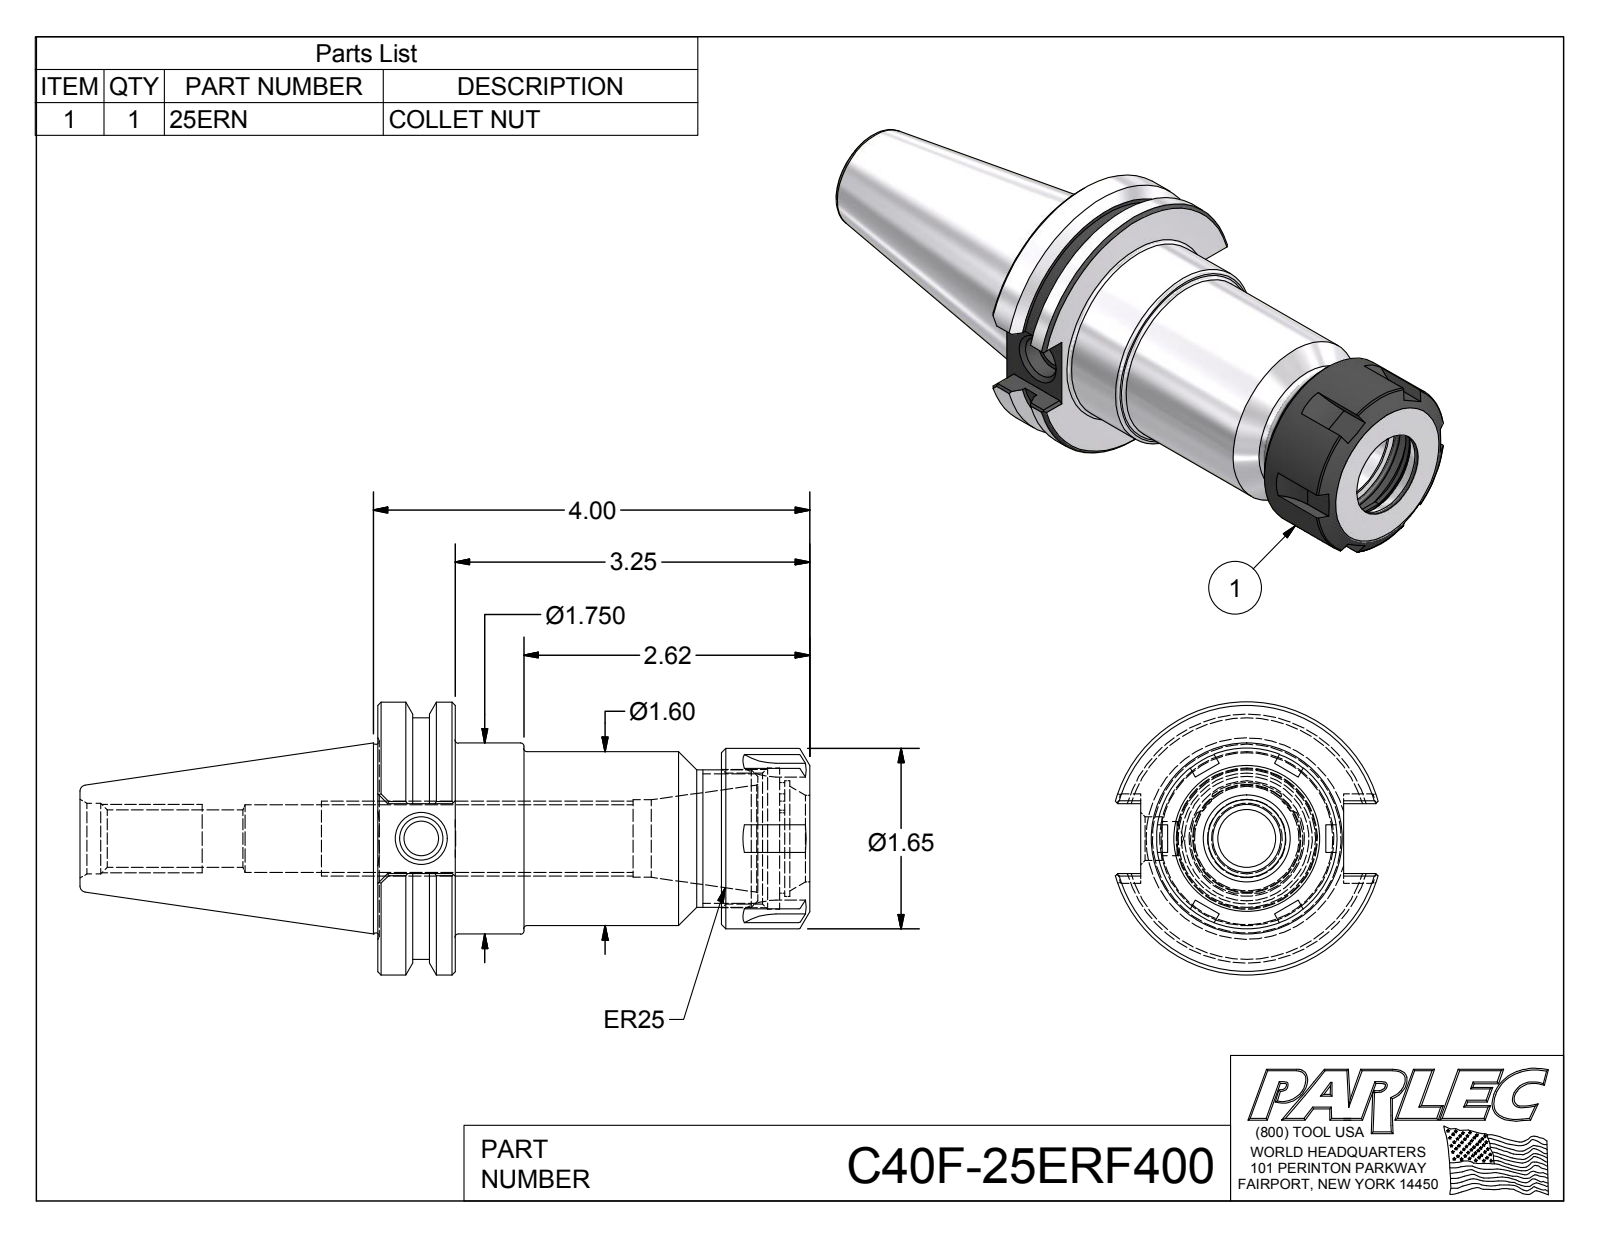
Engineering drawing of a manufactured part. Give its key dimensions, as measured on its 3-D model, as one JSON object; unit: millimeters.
{"part_name": "C40F-25ER4-1; 25ERN; C40F-25ERF400", "step_written_by": "Autodesk Inventor 2016 (AUTOMOTIVE_DESIGN)", "units": "millimeters", "bodies": {"solids": 2, "faces": 160, "planar": 68, "cylindrical": 34, "other": 58}, "overall_size": [169.86, 63.5, 61.11], "volume_mm3": 182671, "surface_area_mm2": 39440, "round_holes": [[8, 1], [10.13, 1], [13.39, 1], [15.75, 1], [16.46, 1], [18.03, 1], [20.32, 1], [30.5, 1], [32.88, 1]], "round_bosses_or_shafts": [[63.5, 1], [56.26, 1], [44.45, 1], [42, 1], [40.51, 1], [32, 1]], "partial_cylinders_radius": [[0.51, 12], [12, 1], [13.06, 1], [13.43, 1]], "face_to_face_distances": [18.04, 100.59, 82.55, 80.01, 61.97, 20.58, 93.49, 75.45, 13.48, 7.1]}
